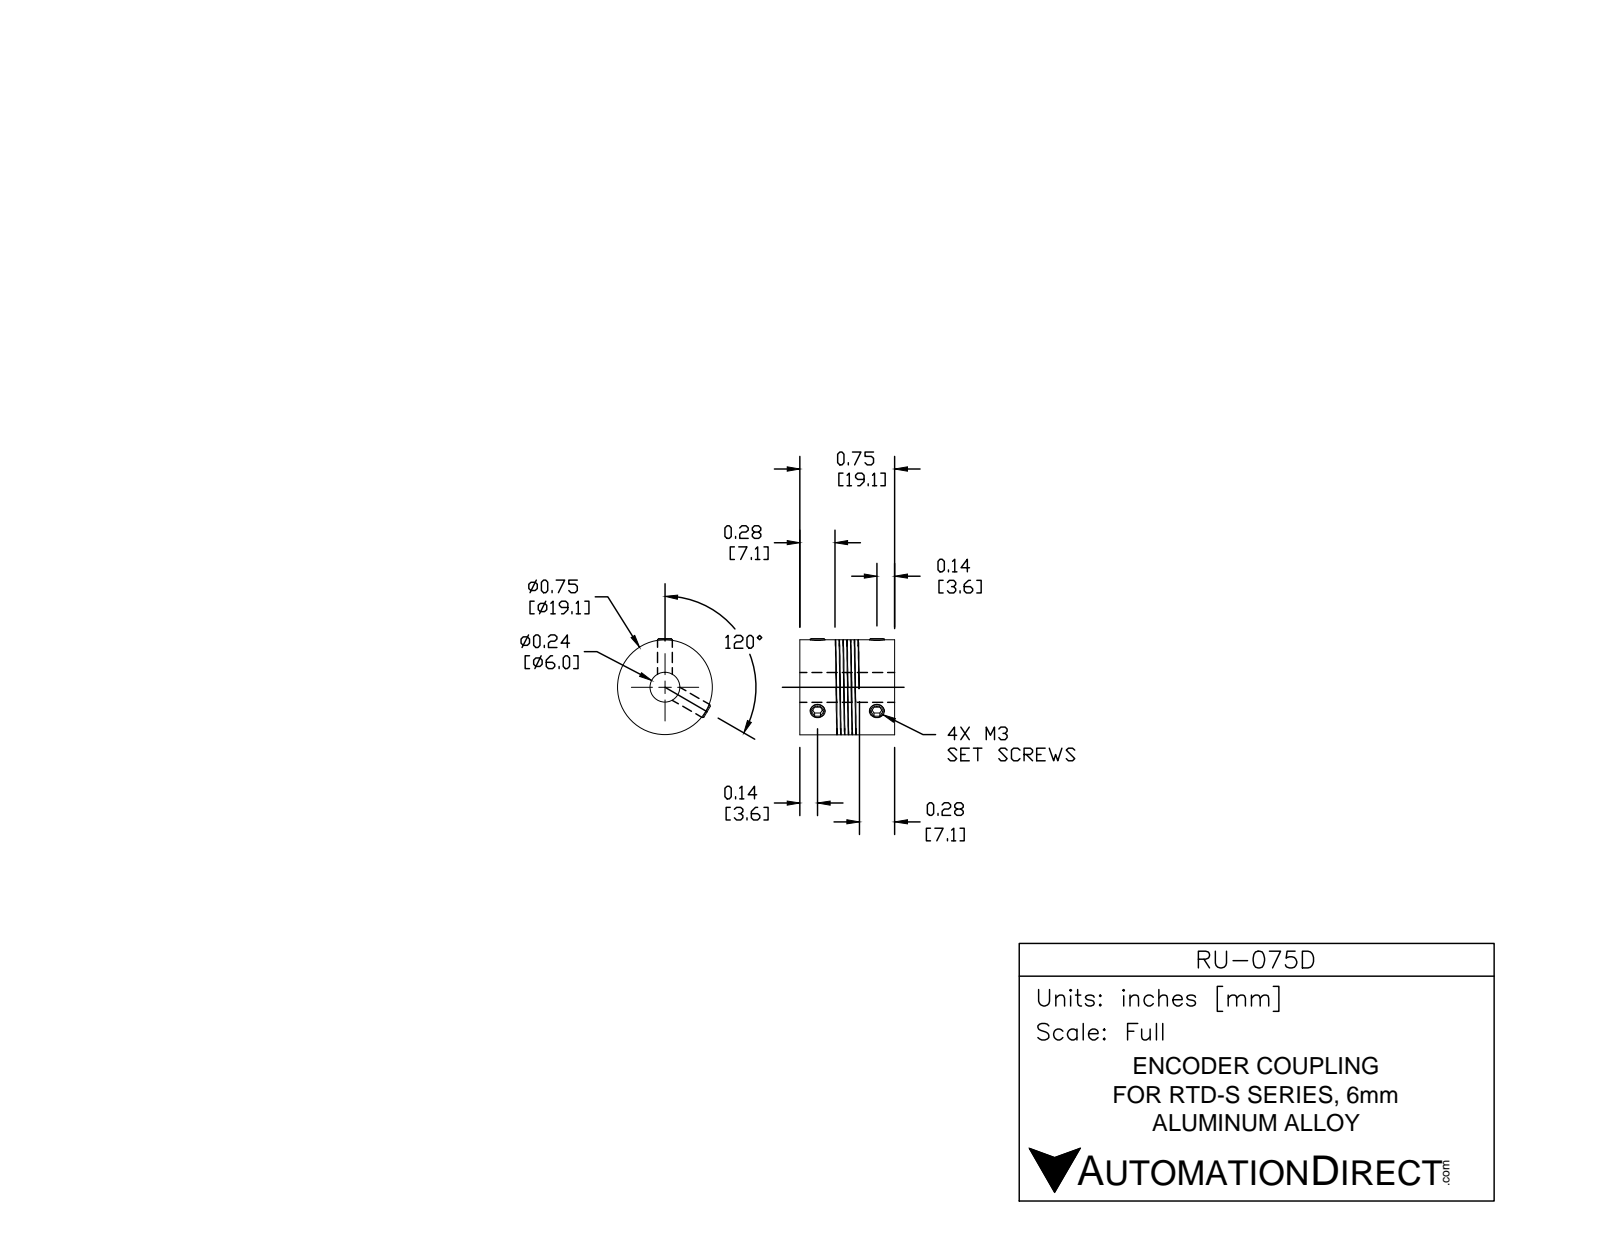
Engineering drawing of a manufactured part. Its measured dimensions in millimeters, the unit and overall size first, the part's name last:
Units: millimetres
Overall size (bounding box): 19.1 × 19.1 × 19.1
Round holes (diameter × count): ⌀3 ×4, ⌀6 ×1, ⌀8 ×1
Round bosses / shafts (diameter × count): ⌀19.1 ×1
Main face-to-face distances: 19.1, 4.6, 14.5, 9.9, 1.5, 12.38, 13.88, 10.88, 0.75, 6
Hole centre spacings: 14.3
Volume: 4 072 mm³ · Surface area: 4 151 mm²
Bodies: 1 solid, 138 faces (58 planar, 40 cylindrical, 40 other)
Part name (STEP PRODUCT): RU-075D
STEP written by: SolidWorks 2016 (AUTOMOTIVE_DESIGN)
